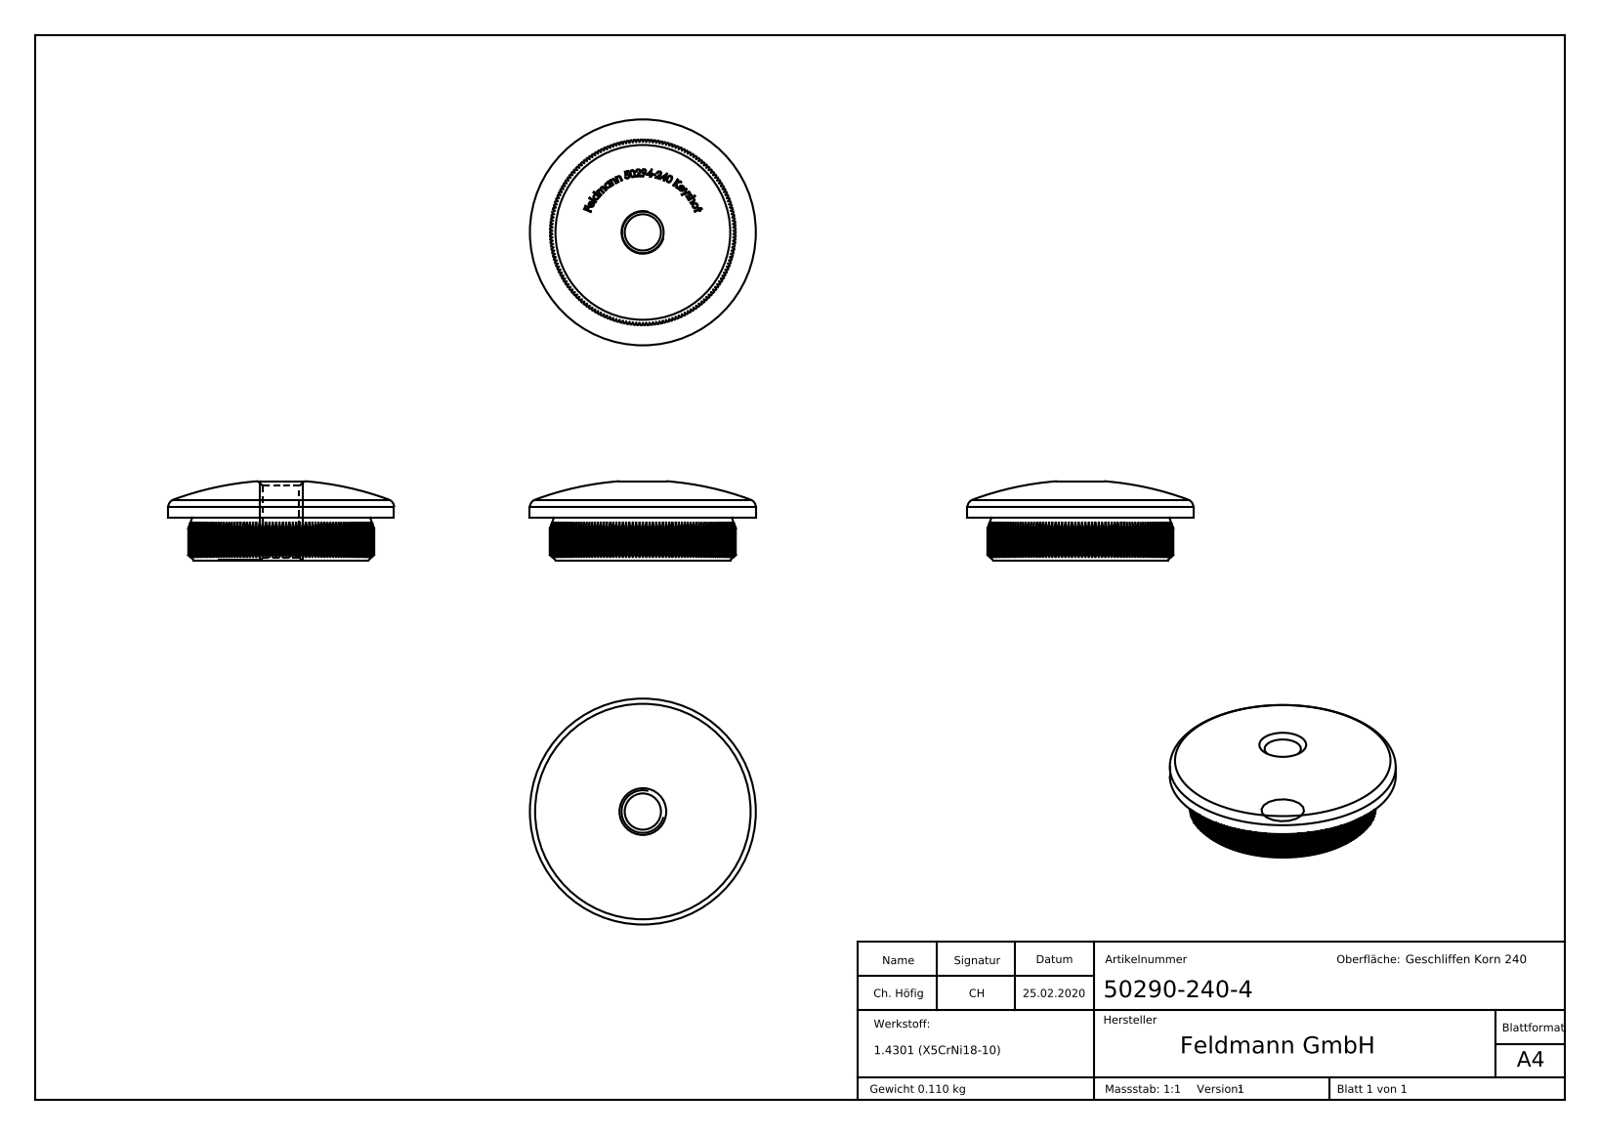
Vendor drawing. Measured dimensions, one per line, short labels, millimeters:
name: 50290-240-4
written by: SolidWorks 2015 (CONFIG_CONTROL_DESIGN)
unit: mm
bodies: 1 solid, 753 faces (472 planar, 174 cylindrical, 107 other)
size: 42.4 × 42.4 × 14.83
volume: 13 925 mm³; area: 4 750 mm²
holes: 1× ⌀6.8
bosses: 1× ⌀42.4
rounds: 1× R17.4
face distances: 8, 17.06, 17.04, 7.9, 17.08, 0.66, 0.54, 0.67, 0.79, 0.72
